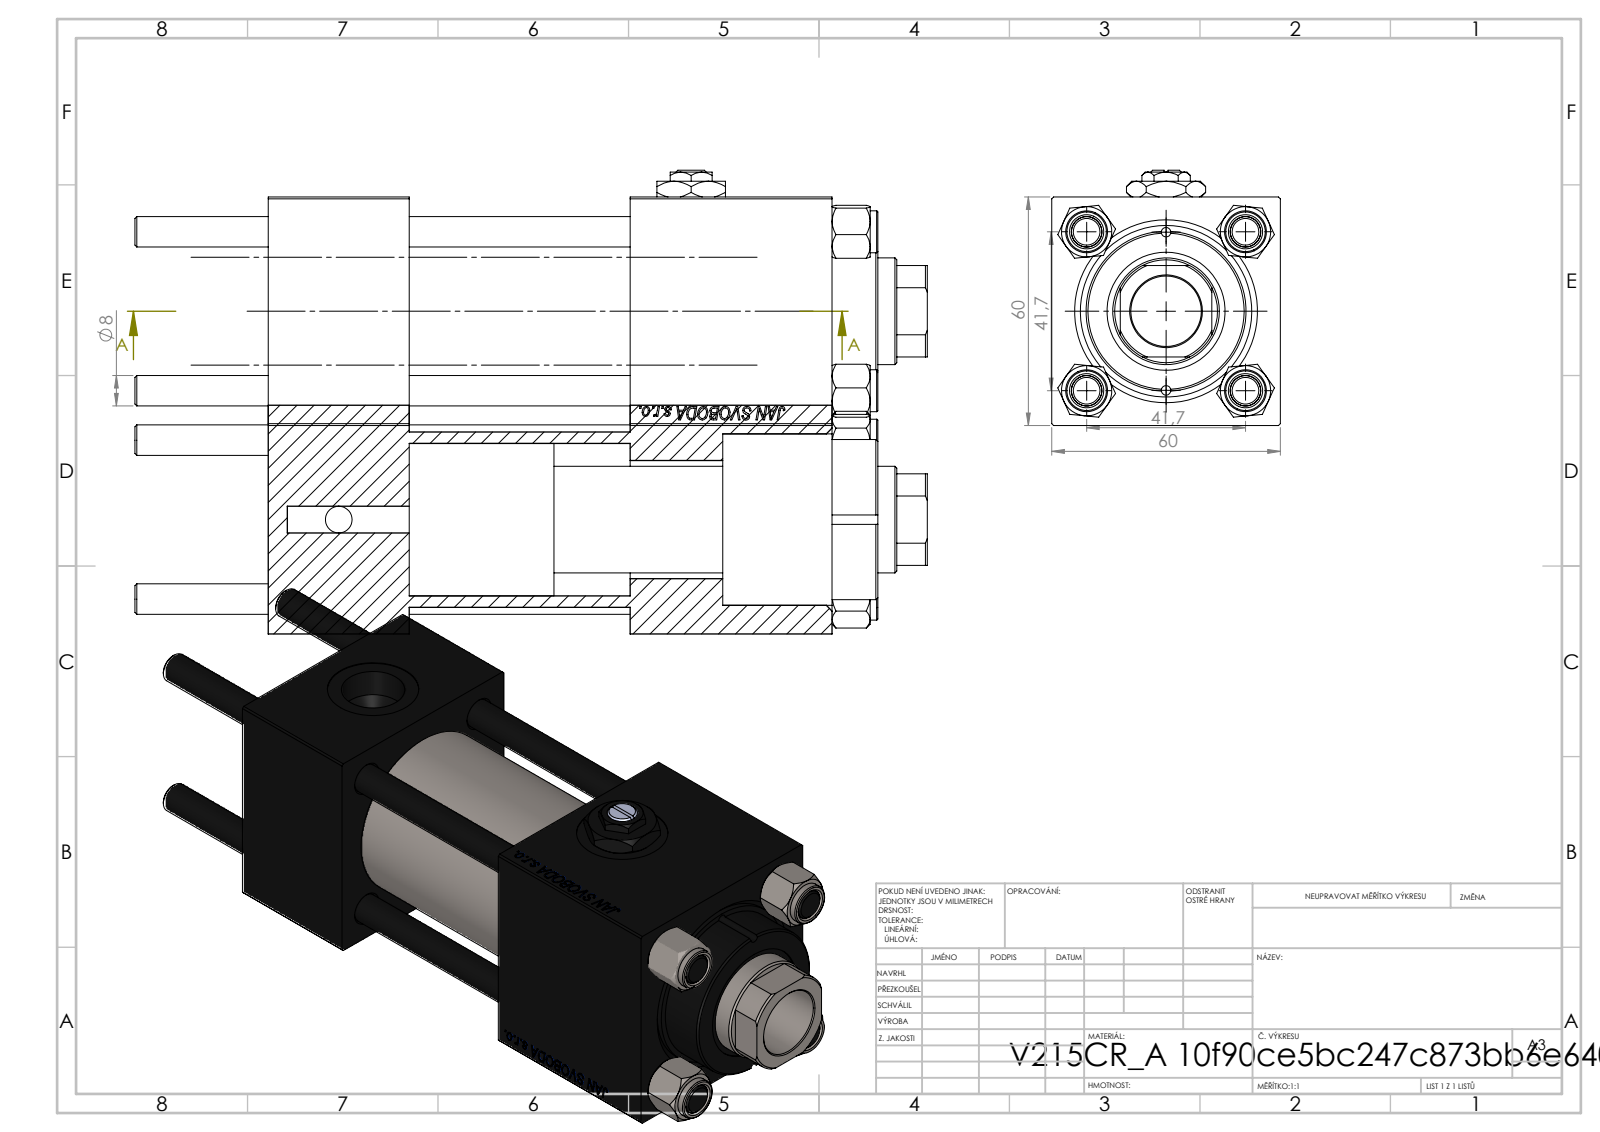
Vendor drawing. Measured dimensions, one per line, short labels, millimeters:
name: V215_VC_A; Zatka_pro_OIL_PORT; CR025_012_A_0_G_A_G_M_020_+#_##_TYCINKA; V215CR_BODY_A (+2 more)
written by: SolidWorks 2019 (CONFIG_CONTROL_DESIGN)
unit: mm
bodies: 12 solids, 1188 faces (546 planar, 86 cylindrical, 556 other)
size: 208 × 67 × 60
volume: 433 537 mm³; area: 121 499 mm²
holes: 4× ⌀8, 2× ⌀2.5, 2× ⌀7, 2× ⌀16.66, 2× ⌀24, 1× ⌀18.5, 1× ⌀28, 1× ⌀31, 1× ⌀40, 1× ⌀45
bosses: 4× ⌀11, 1× ⌀46, 1× ⌀42
rounds: 1× R13.5
face distances: 60, 37, 58, 95, 53, 148, 111, 119.3, 82.3, 24.3
hole spacings: 20.85, 29.49, 41.7, 46.53, 20.75, 58.97, 41.5, 92.5
